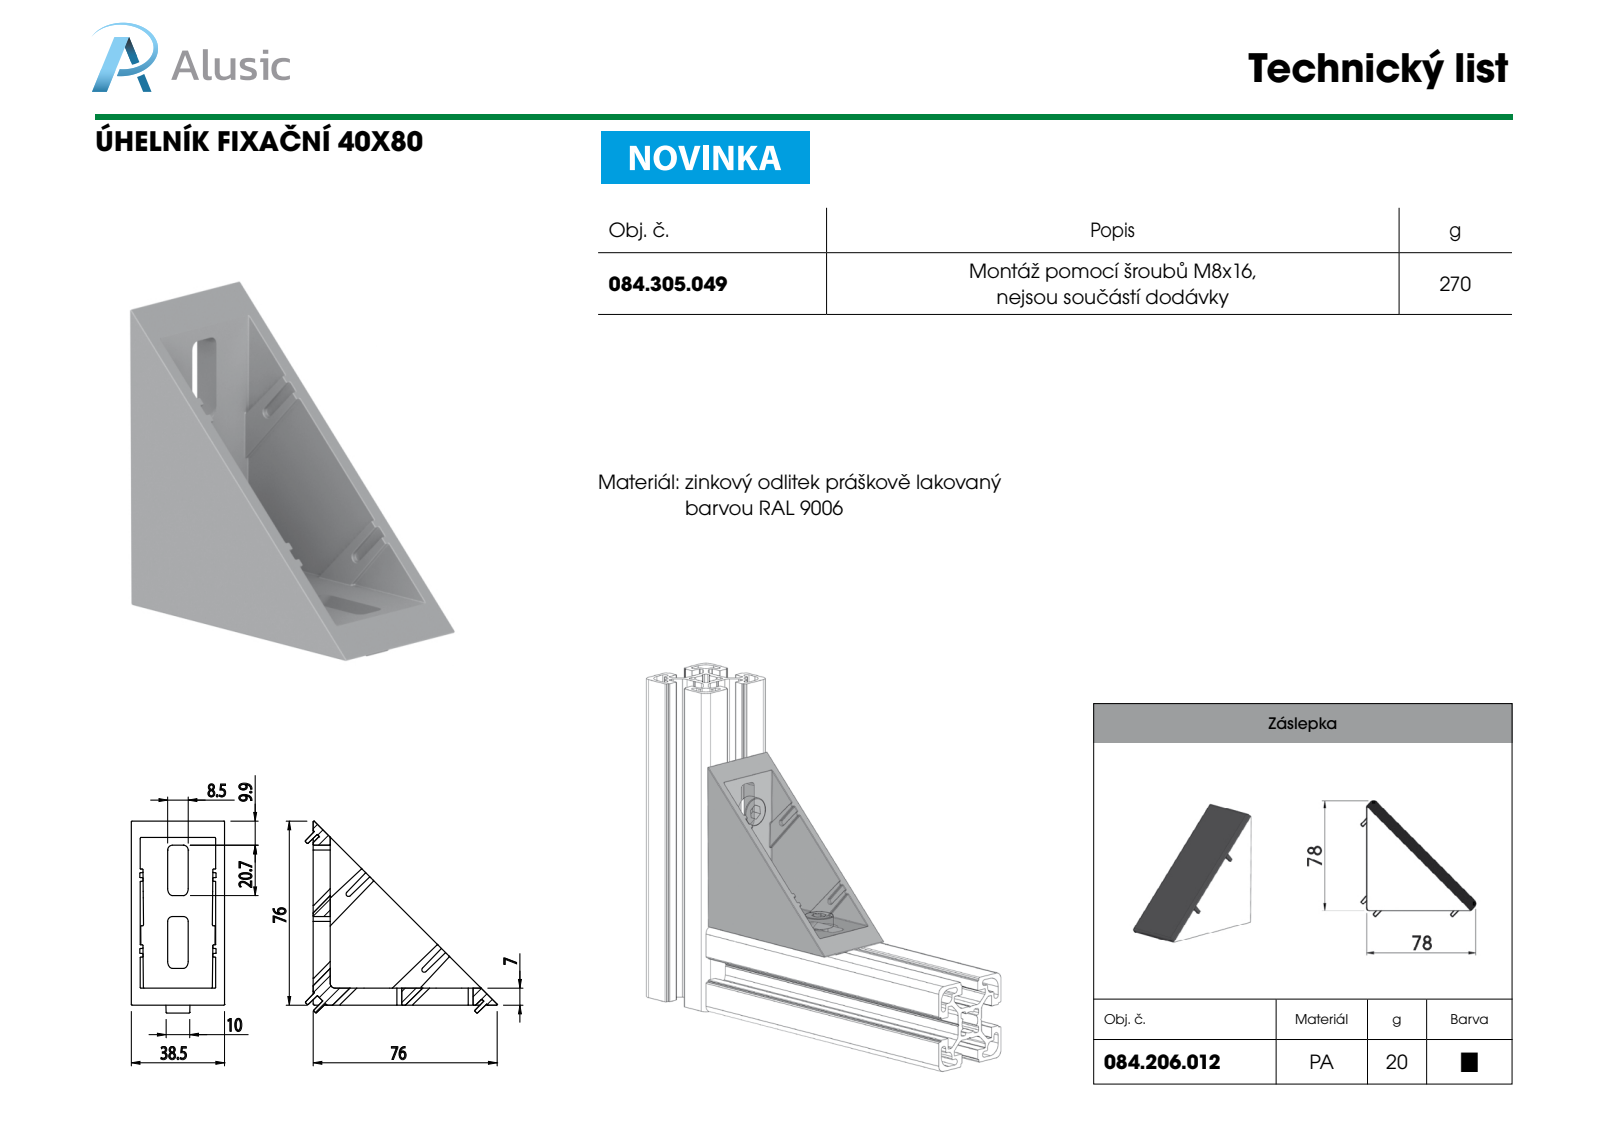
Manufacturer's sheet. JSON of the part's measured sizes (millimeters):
{"part_name": "084.305.049", "step_written_by": "SolidWorks 2018 (AUTOMOTIVE_DESIGN)", "units": "millimeters", "bodies": {"solids": 1, "faces": 714, "planar": 149, "cylindrical": 309, "other": 256}, "overall_size": [78.82, 78.82, 38.3], "volume_mm3": 40790, "surface_area_mm2": 22879, "partial_cylinders_radius": [[0.3, 183], [0.5, 45], [2, 17], [1.3, 2]], "face_to_face_distances": [3.65, 7, 3, 4, 4.8, 11.69, 1.15, 5.67, 6.82, 10.47]}
